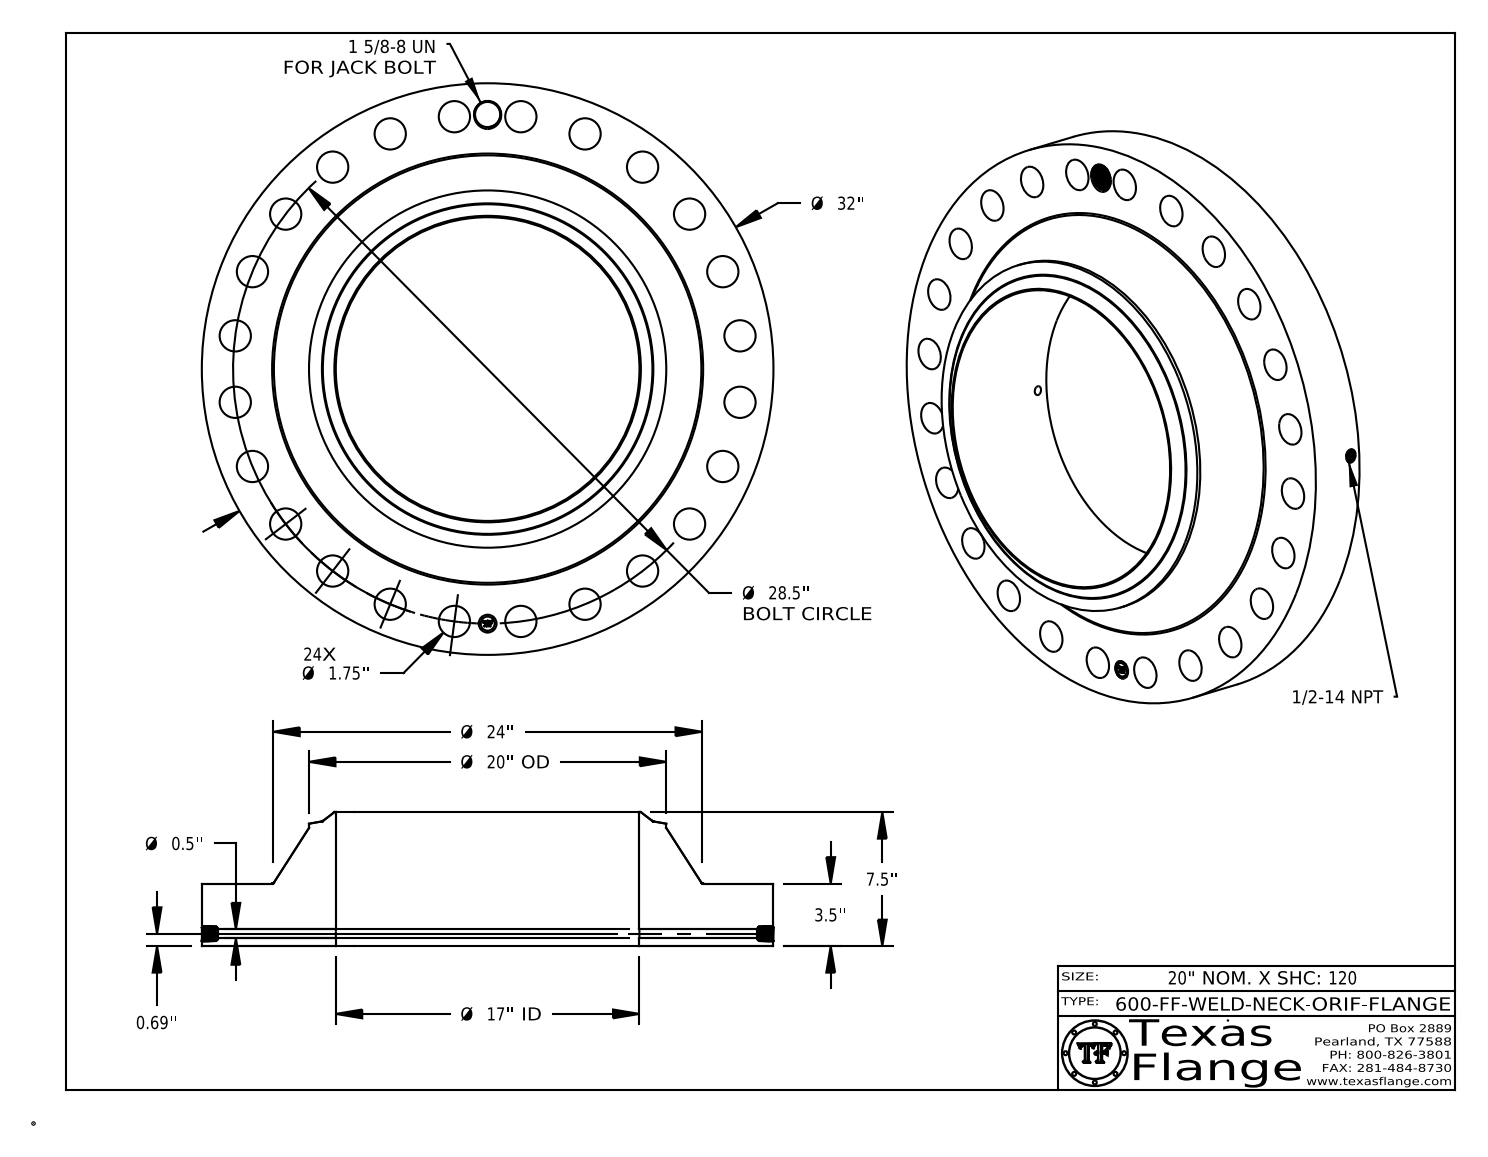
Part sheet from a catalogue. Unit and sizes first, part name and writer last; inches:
Units: inches
Overall size (bounding box): 32 × 32 × 7.5
Round holes (diameter × count): ⌀1.75 ×24, ⌀0.5 ×1, ⌀0.672 ×1, ⌀1 ×1, ⌀1.409 ×1, ⌀17 ×1
Round bosses / shafts (diameter × count): ⌀0.061 ×8, ⌀32 ×1, ⌀20 ×1, ⌀0.788 ×1
Main face-to-face distances: 3.5, 7.5, 4, 3.485, 0.015, 4.015, 0.298, 0.293, 0.054, 0.248
Hole centre spacings: 14.25, 17.35, 24.681, 28.256, 10.906, 3.72, 7.376, 20.152
Volume: 2 330 in³ · Surface area: 2 452 in²
Bodies: 1 solid, 880 faces (368 planar, 149 cylindrical, 363 other)
Part name (STEP PRODUCT): 600-FF-WELD-NECK
STEP written by: CATIA V5 STEP AP214 (AUTOMOTIVE_DESIGN)
